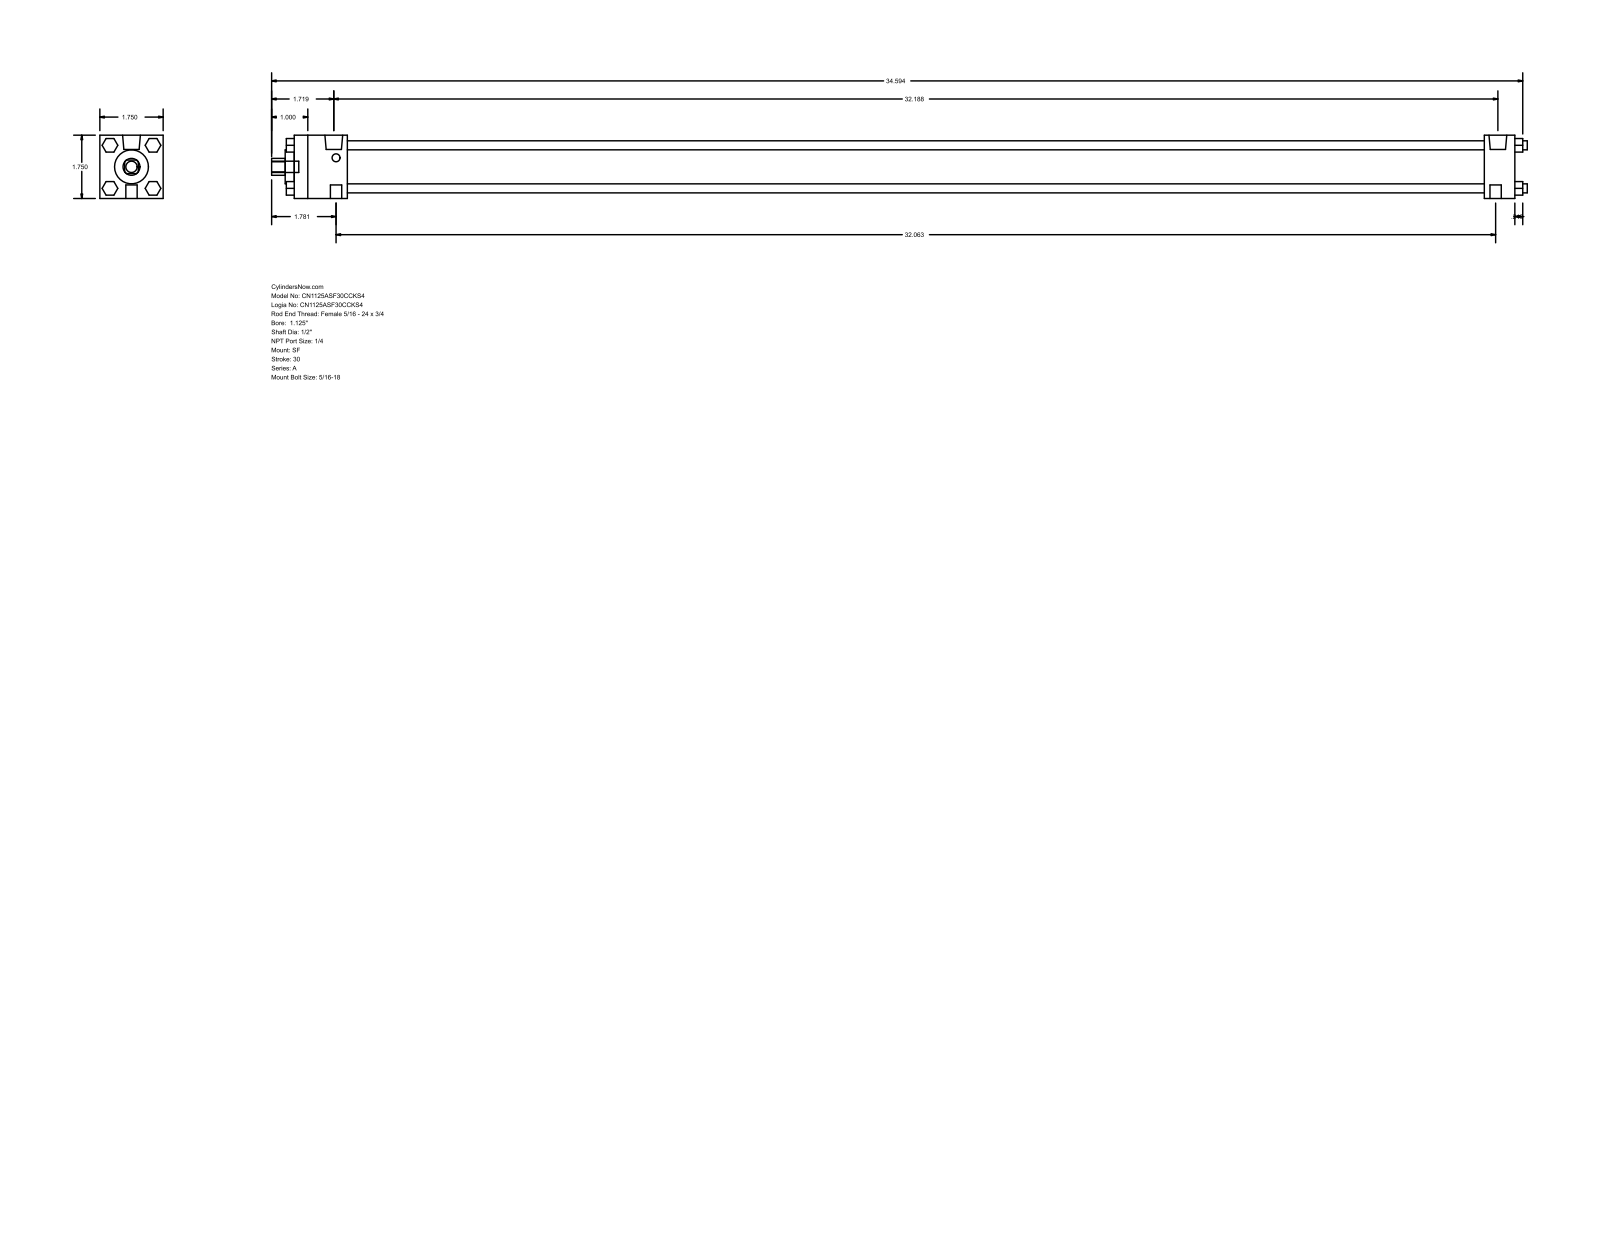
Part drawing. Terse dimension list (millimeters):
name: A_SF__0112_0.5
written by: GSSL Pune (CONFIG_CONTROL_DESIGN)
unit: mm
bodies: 0 solids, 120 faces (92 planar, 28 cylindrical, 0 other)
size: 881.86 × 44.45 × 44.45
holes: 1× ⌀12.7, 1× ⌀23.81, 1× ⌀31.88
bosses: 4× ⌀6.35, 3× ⌀7.94, 2× ⌀12.49, 2× ⌀5.56
rounds: 1× R5.94
face distances: 44.46, 857.24, 835.81, 21.43, 37.3, 798.51, 819.94, 9.53, 5.59, 9.52
